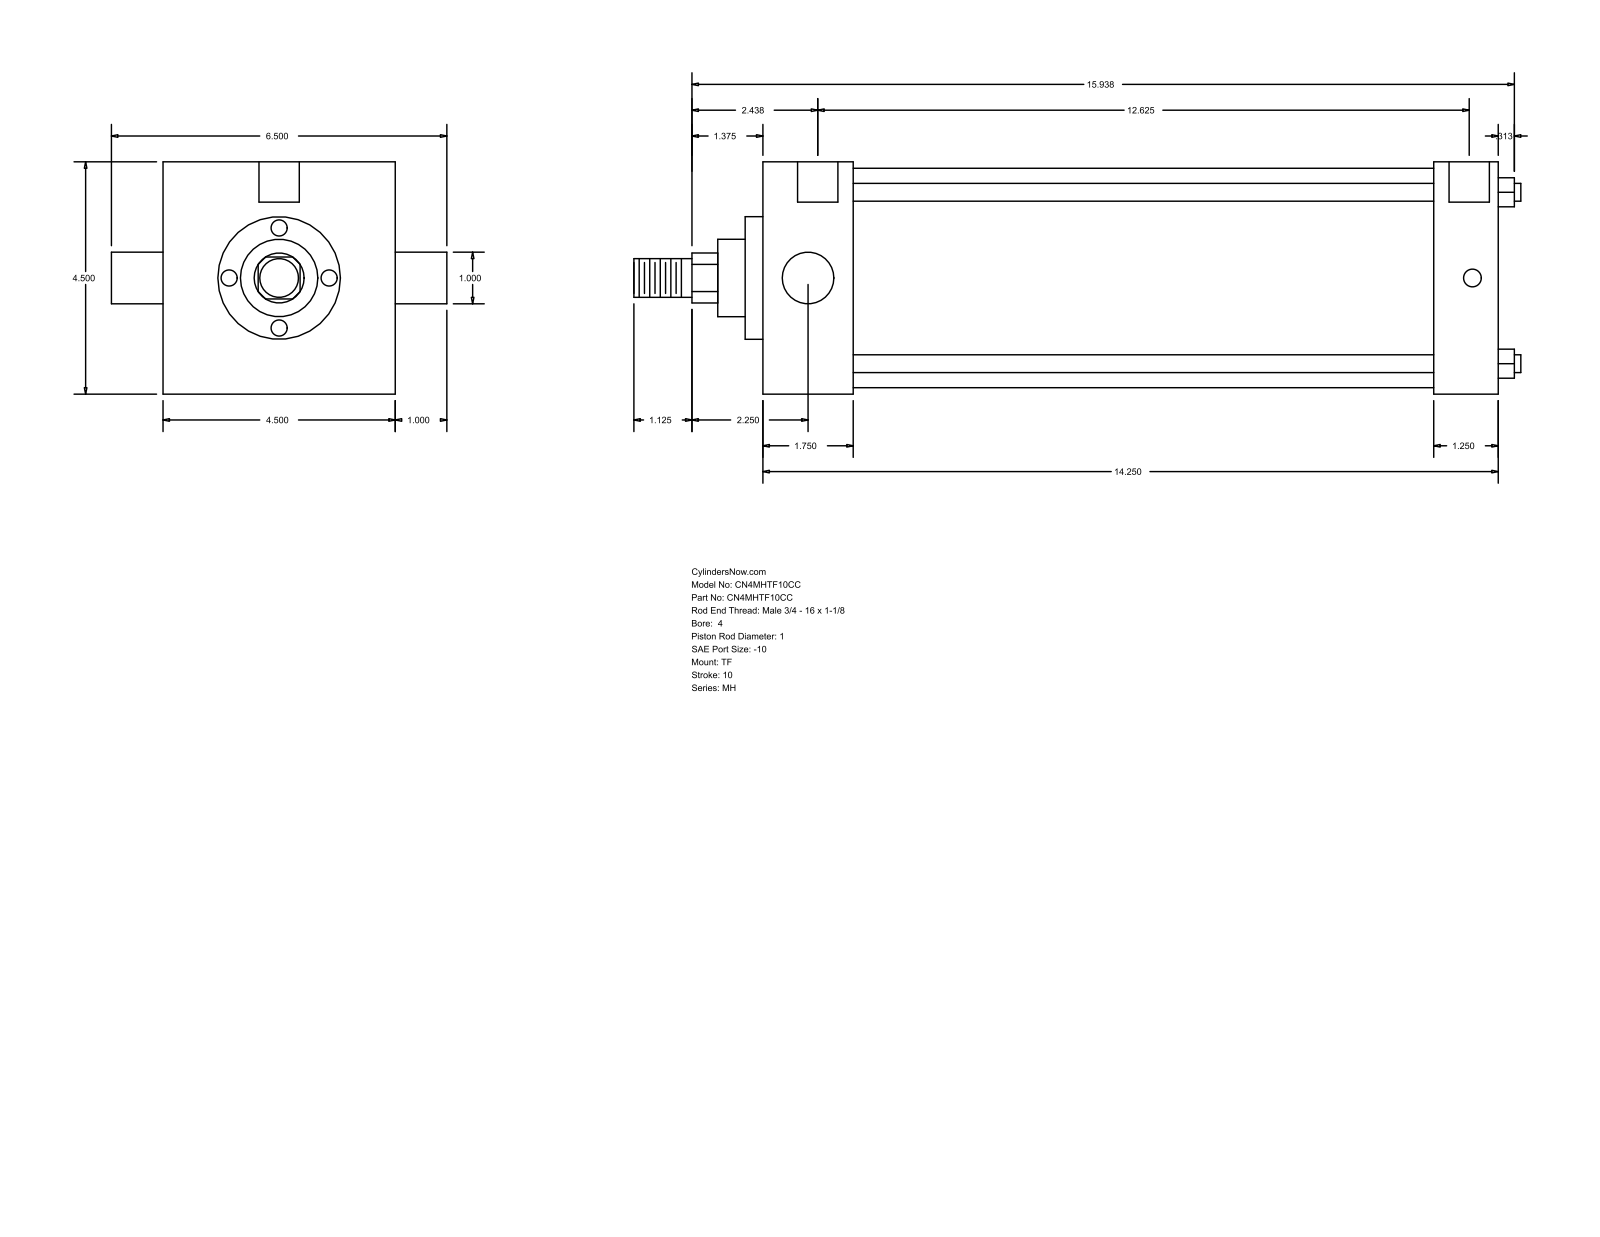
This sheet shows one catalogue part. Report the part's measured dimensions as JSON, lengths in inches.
{"part_name": "MH_TF__0400_1", "step_written_by": "GSSL Pune (CONFIG_CONTROL_DESIGN)", "units": "inches", "bodies": {"solids": 0, "faces": 86, "planar": 61, "cylindrical": 25, "other": 0}, "overall_size": [17.187, 6.5, 4.5], "round_holes": [[0.344, 3], [0.781, 2]], "round_bosses_or_shafts": [[0.345, 4], [1, 2], [4.25, 1], [2.375, 1], [1.5, 1], [0.75, 1]], "partial_cylinders_radius": [[0.484, 1]], "face_to_face_distances": [4.5, 14.25, 1.75, 12.5, 13, 11.25, 1.25, 0.344, 2.094, 13.344], "hole_center_spacings": [0.062, 0.063, 12.625, 12.687, 12.688, 12.75]}
